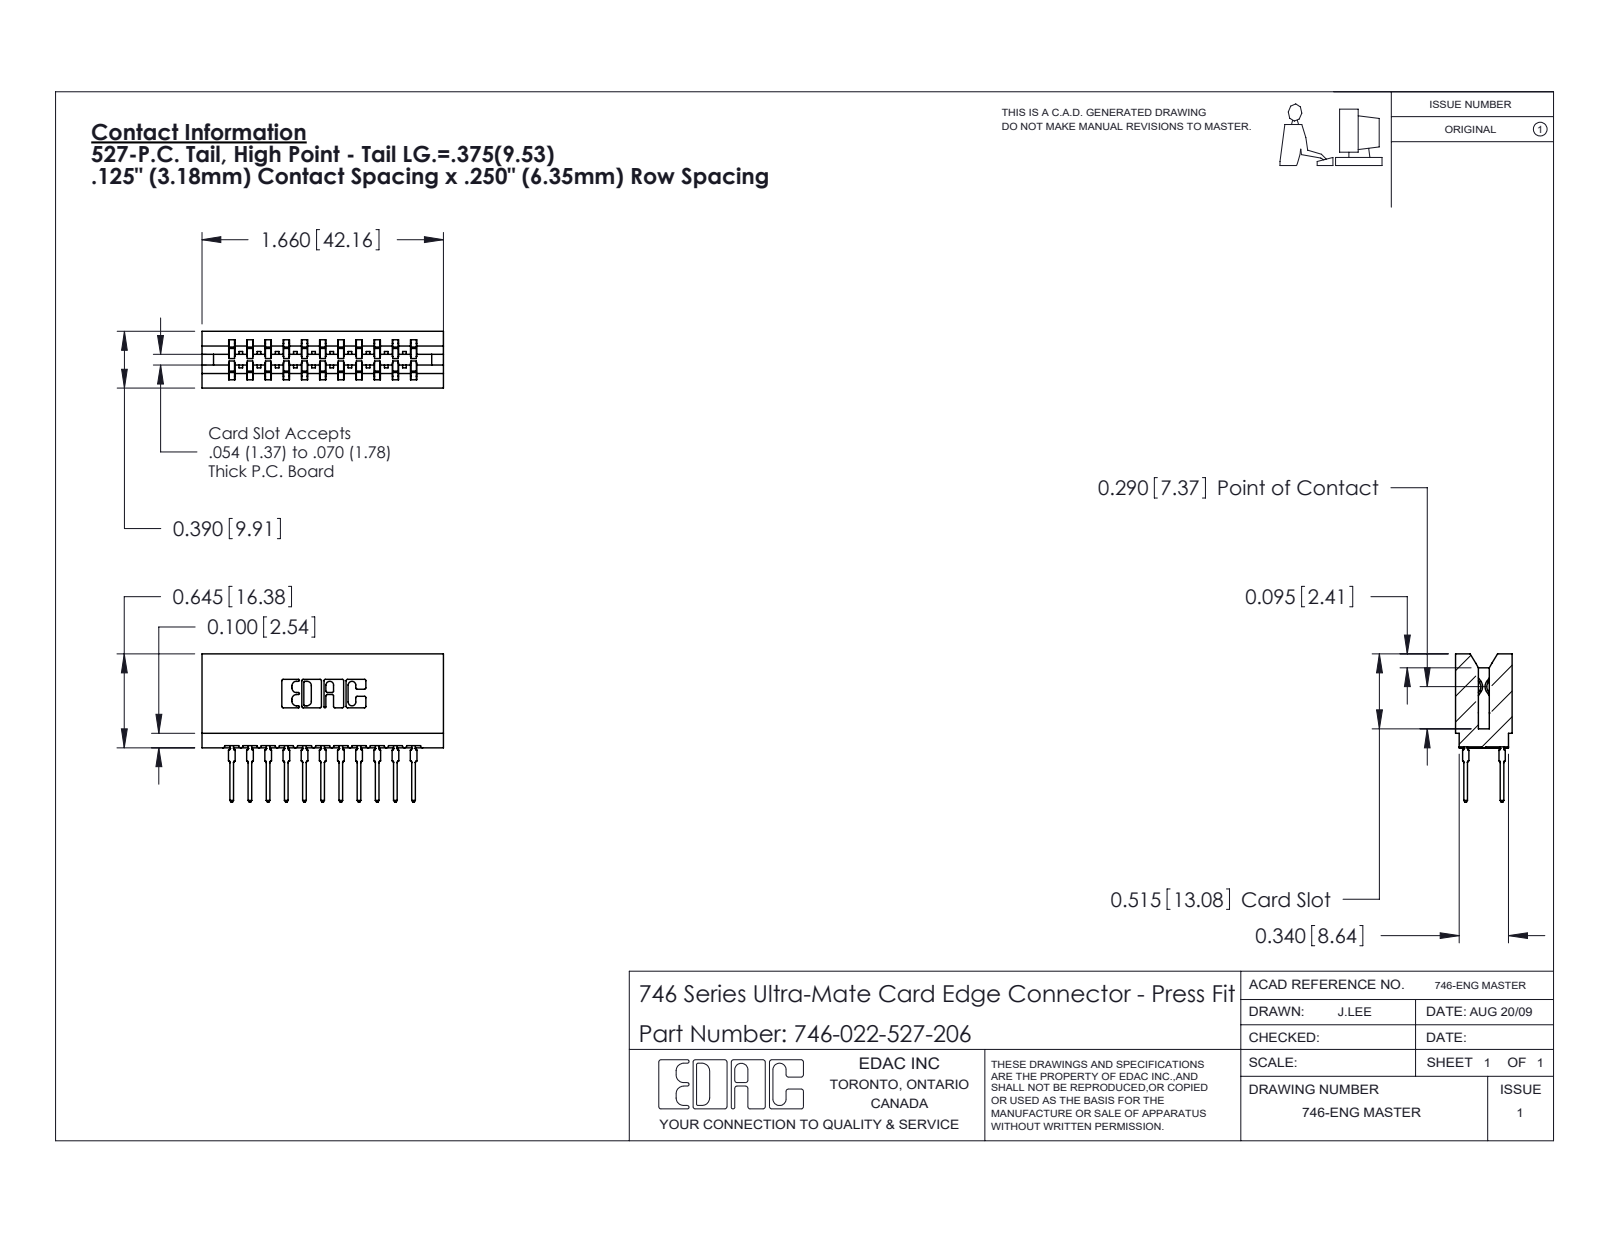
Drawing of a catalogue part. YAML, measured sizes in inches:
part_name: "746-022-527-206; 746-292-001_527; 746 Part_.515 Slot Depth - 06"
step_written_by: "SolidWorks 2020 (CONFIG_CONTROL_DESIGN)"
units: inches
bodies: {solids: 23, faces: 2067, planar: 1068, cylindrical: 427, other: 572}
overall_size: [1.66, 1.019, 0.39]
volume: 0.289
surface_area: 11.11
partial_cylinders:
  - {radius: 0.021, count: 44}
  - {radius: 0.01, count: 22}
  - {radius: 0.015, count: 12}
  - {radius: 0.005, count: 8}
  - {radius: 0.011, count: 8}
  - {radius: 0.007, count: 6}
  - {radius: 0.031, count: 6}
  - {radius: 0.026, count: 3}
face_to_face_distances: [0.25, 0.333, 0.057, 0.5, 0.125, 0.125, 0.39, 0.042, 0.208, 0.458]
